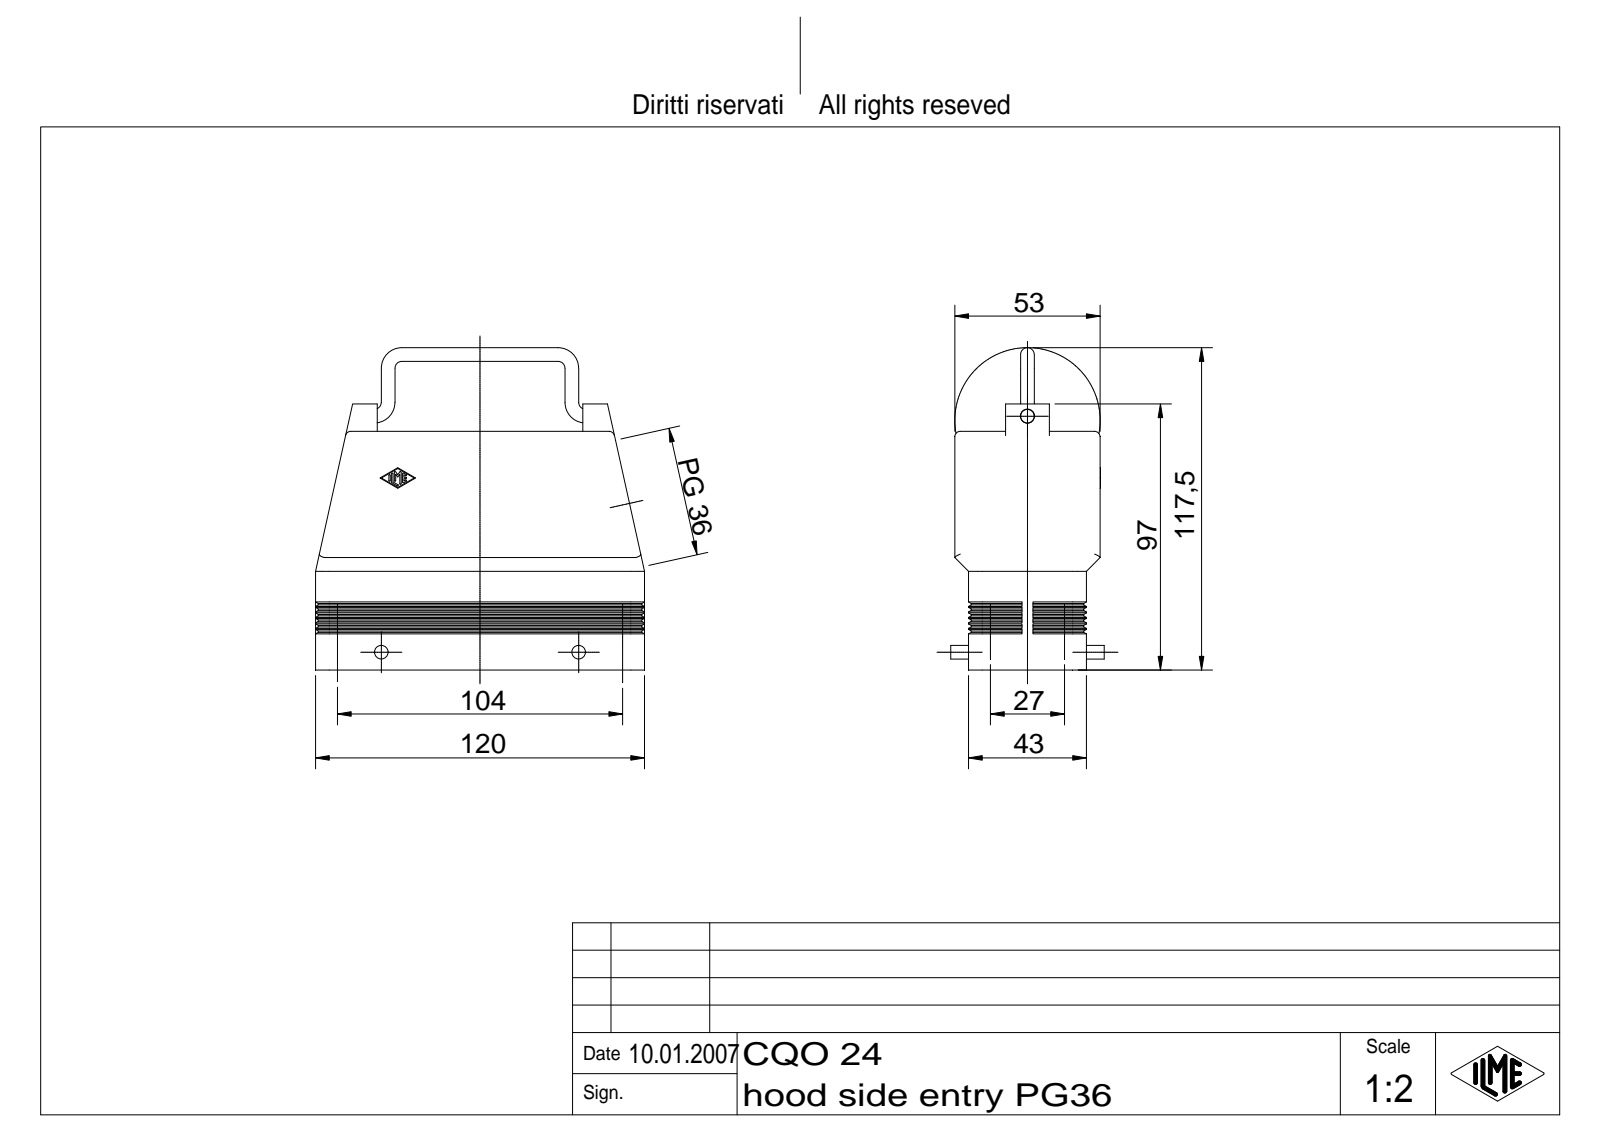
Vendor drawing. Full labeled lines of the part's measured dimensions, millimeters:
Part name (STEP PRODUCT): CQO 24
STEP written by: Autodesk Inventor 7 (AUTOMOTIVE_DESIGN)
Units: millimetres
Bodies: 1 solid, 464 faces (166 planar, 140 cylindrical, 158 other)
Overall size (bounding box): 120 × 117.5 × 56
Volume: 93 681 mm³ · Surface area: 68 642 mm²
Round holes (diameter × count): ⌀5.2 ×1, ⌀45.48 ×1
Round bosses / shafts (diameter × count): ⌀5 ×6
Partial cylindrical surfaces — rounded edges, fillets, slot ends (radius × count): R2 ×16, R0.25 ×14, R2.5 ×4, R5 ×4, R4 ×2
Main face-to-face distances: 3, 5, 45, 50, 42, 8, 40, 2, 47, 48
